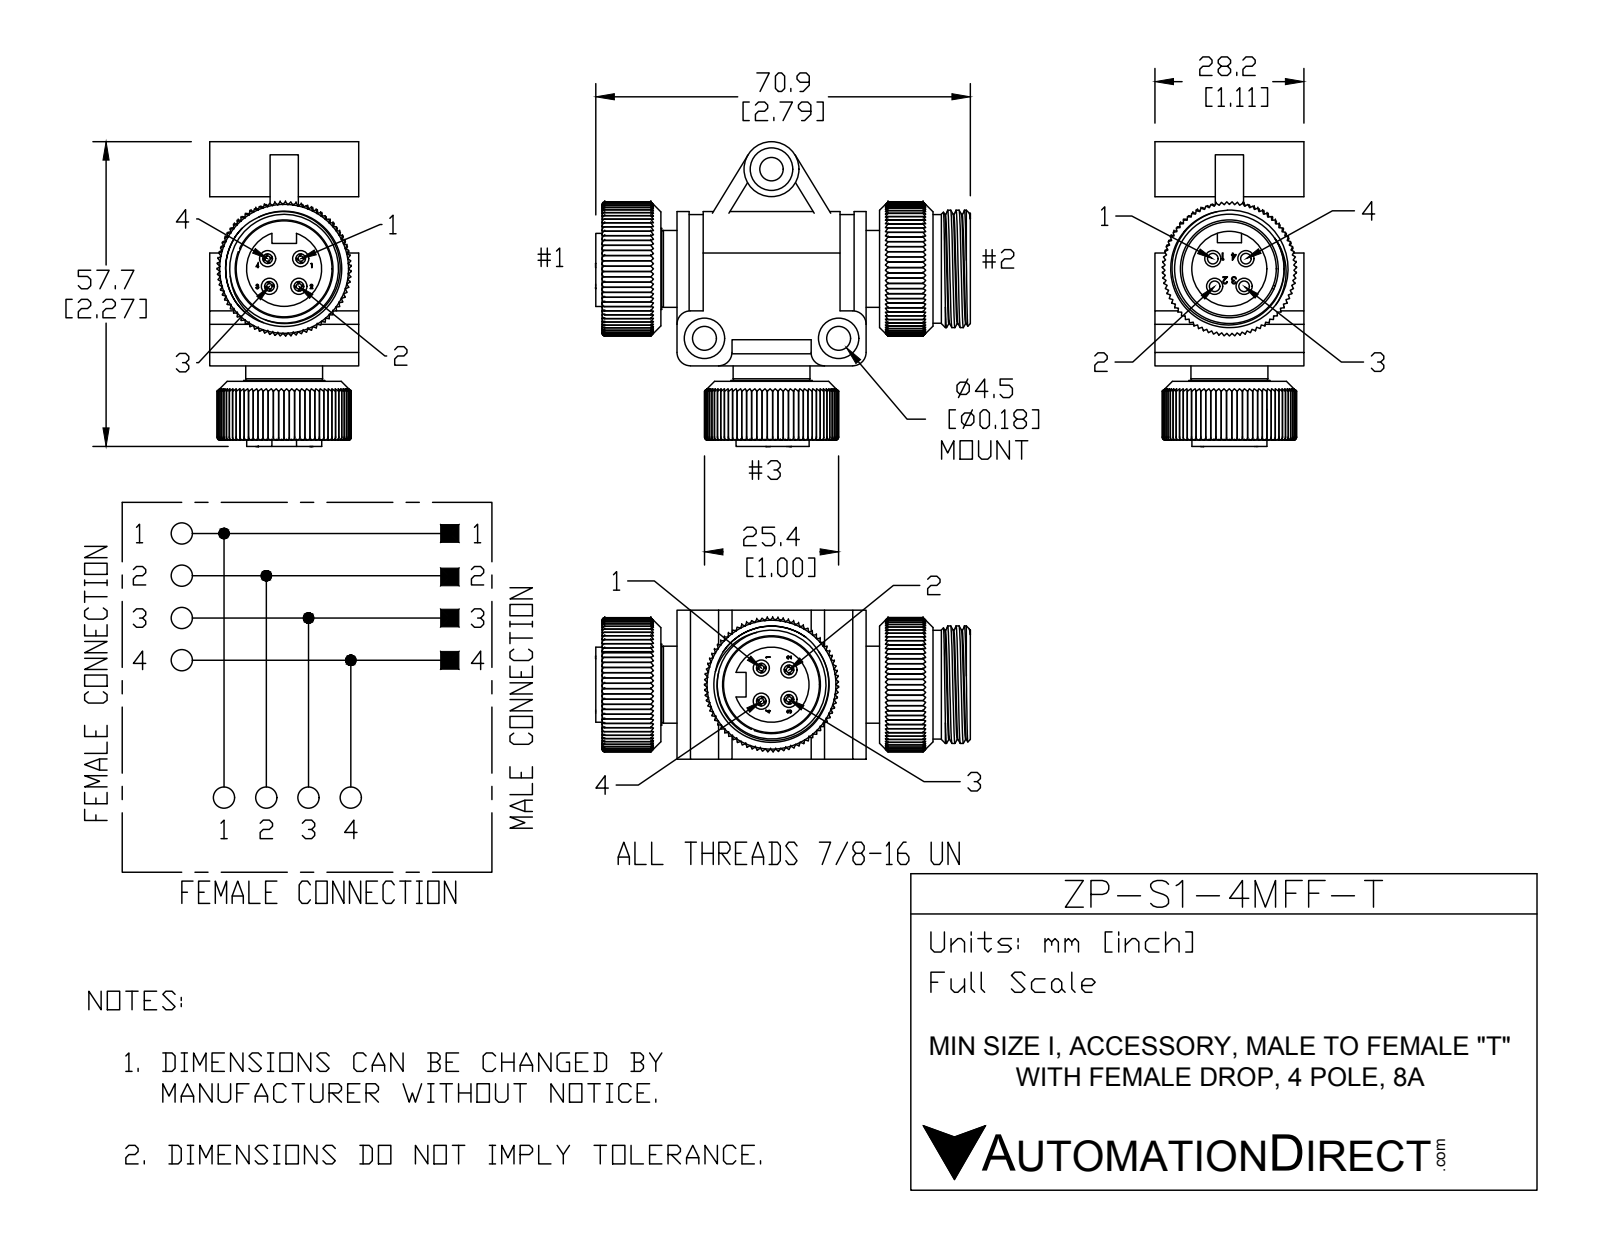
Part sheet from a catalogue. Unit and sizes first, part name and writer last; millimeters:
Units: millimetres
Overall size (bounding box): 70.98 × 57.72 × 28.19
Round holes (diameter × count): ⌀3.05 ×8, ⌀3.66 ×4, ⌀4.5 ×2, ⌀7 ×2, ⌀7.62 ×2, ⌀20.57 ×2, ⌀22.4 ×2, ⌀4.44 ×1, ⌀8.08 ×1, ⌀15.87 ×1, ⌀15.88 ×1, ⌀18.54 ×1
Round bosses / shafts (diameter × count): ⌀2 ×4, ⌀18.14 ×2, ⌀17.54 ×2, ⌀14.55 ×2, ⌀14.22 ×2, ⌀13.62 ×2, ⌀22.22 ×1, ⌀21.72 ×1
Partial cylindrical surfaces — rounded edges, fillets, slot ends (radius × count): R2.54 ×6, R6.73 ×2, R12.7 ×2, R2.29 ×1, R6.48 ×1, R10.86 ×1
Main face-to-face distances: 28.2, 35.82, 2.03, 4.95, 7.01, 4.96, 30.86, 15.36, 21.35, 1.19
Hole centre spacings: 3.67, 4.32, 5.24, 7.89, 5.58, 6.24, 34.44, 25.4
Volume: 39 665 mm³ · Surface area: 18 485 mm²
Bodies: 1 solid, 1362 faces (680 planar, 400 cylindrical, 282 other)
Part name (STEP PRODUCT): MIN-4MFF-T
STEP written by: SolidWorks 2015 (AUTOMOTIVE_DESIGN)
